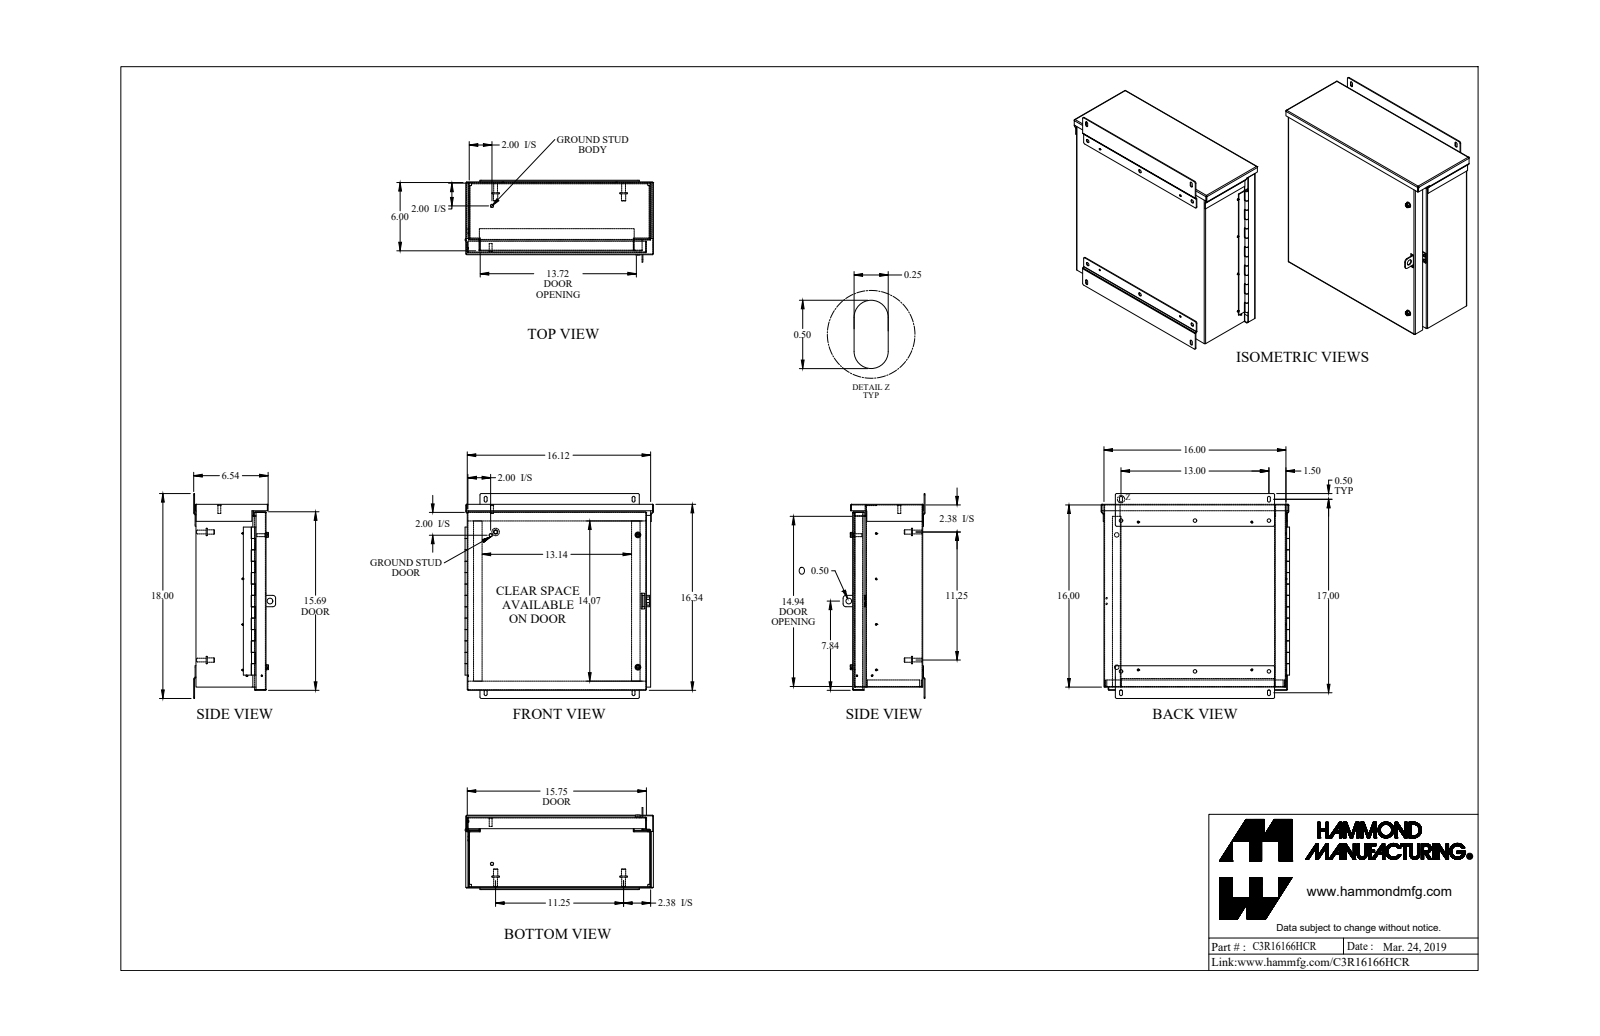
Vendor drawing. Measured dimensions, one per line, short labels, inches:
name: C3R16166HCR_Default
written by: SolidWorks 2019 (CONFIG_CONTROL_DESIGN)
unit: in
bodies: 33 solids, 832 faces (475 planar, 303 cylindrical, 54 other)
size: 18 × 16.556 × 7.197
volume: 79.22 in³; area: 2 561 in²
holes: 9× ⌀0.313, 4× ⌀0.14, 3× ⌀0.26, 2× ⌀0.137, 2× ⌀0.266, 2× ⌀0.28, 2× ⌀0.29, 2× ⌀0.397, 1× ⌀0.188, 1× ⌀0.5
bosses: 10× ⌀0.131, 4× ⌀0.65, 4× ⌀0.375, 4× ⌀0.33, 3× ⌀0.51, 3× ⌀0.244, 3× ⌀0.187, 2× ⌀0.5
rounds: 26× R0.029, 26× R0.086, 19× R0.125, 5× R0.036, 5× R0.108, 3× R0.171, 2× R0.25
face distances: 0.057, 6.1, 6.043, 16, 15.943, 6.157, 16.057, 0.943, 4.943, 15.886
hole spacings: 1.505, 5.002, 6.5, 11.501, 13, 14.045, 17.45, 13.21
